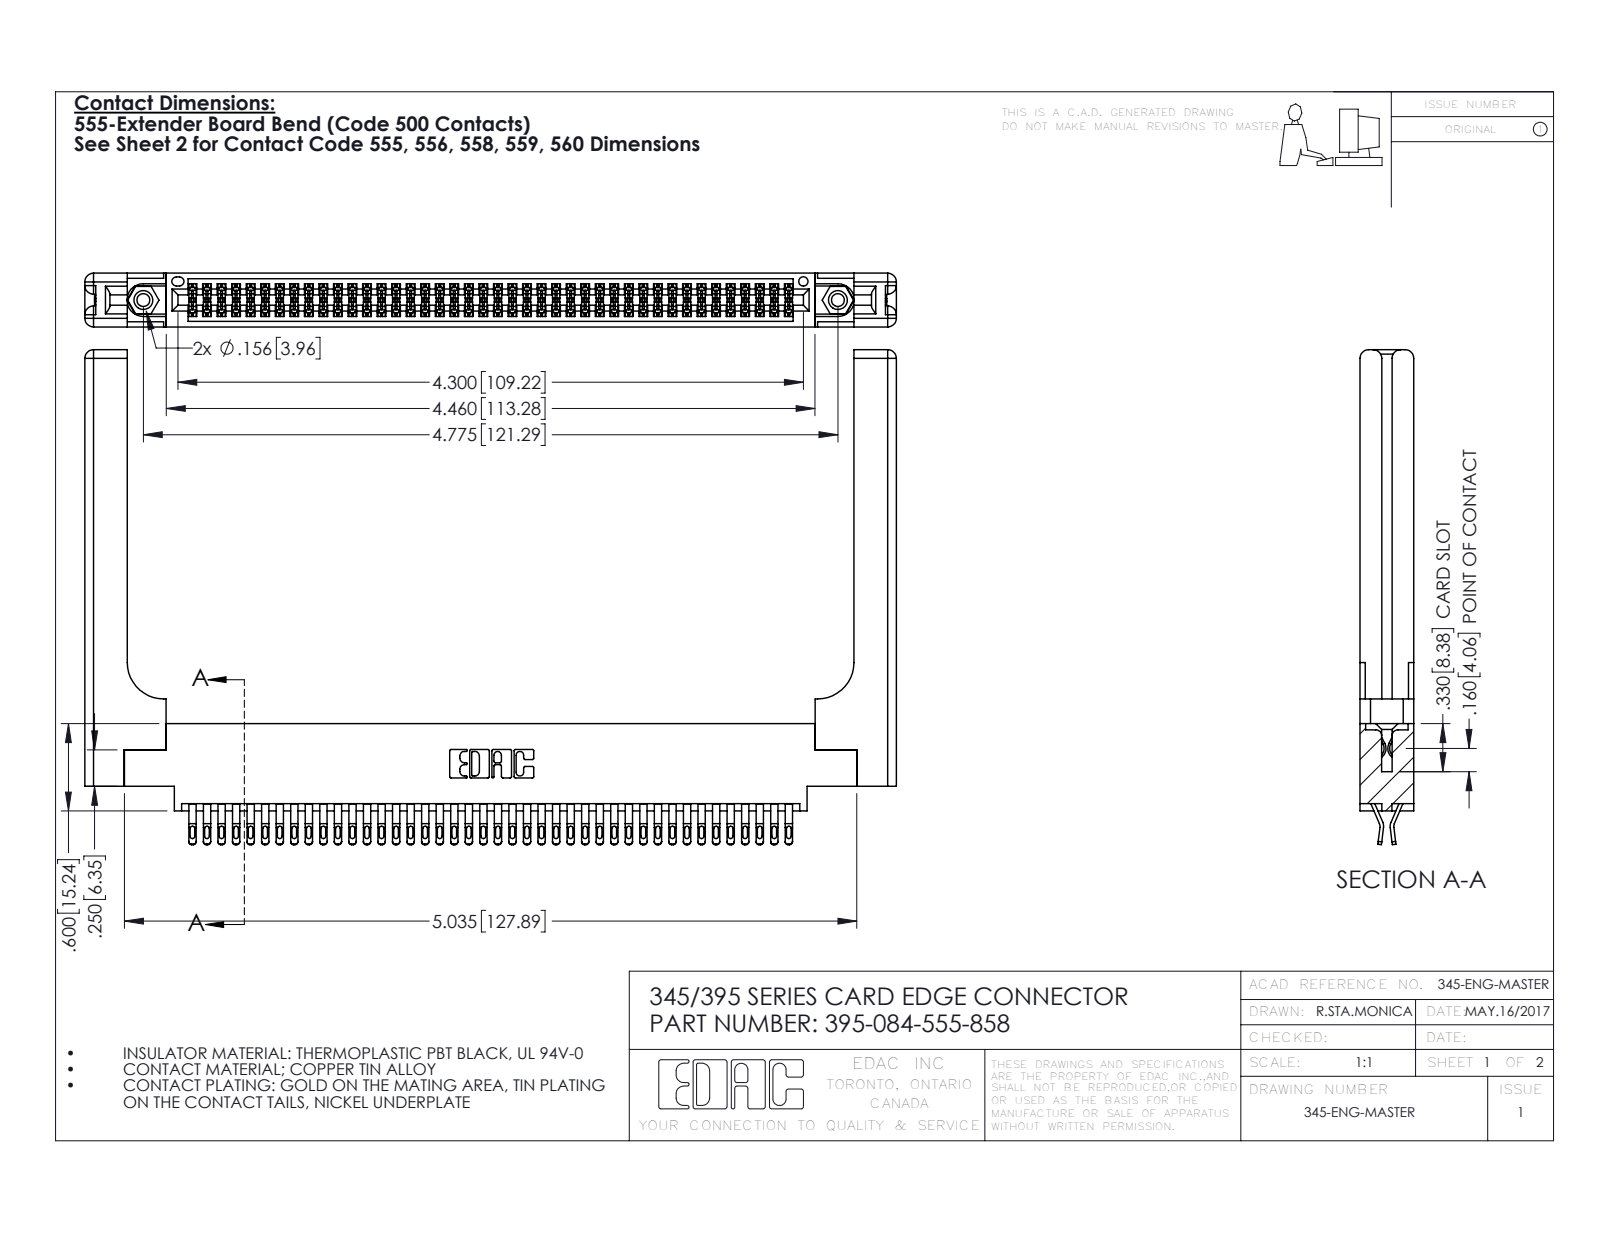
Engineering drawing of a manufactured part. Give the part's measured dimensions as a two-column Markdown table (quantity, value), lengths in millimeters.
| quantity | value |
| --- | --- |
| part name | 345-250-001_345-250-001-102; 345 Part_0.170 Offset - 0.156 Dia-TH; 345-292-001_555 Tail; 345-220-058_345-220-058 (+1 more) |
| STEP written by | SolidWorks 2016 (CONFIG_CONTROL_DESIGN) |
| units | millimeters |
| bodies | 89 solids, 5090 faces (2836 planar, 2194 cylindrical, 60 other) |
| overall size | 141.7 × 86.4 × 9.4 |
| volume | 22 370 mm³ |
| surface area | 26 590 mm² |
| round holes (diameter × count) | 2.3 × 2, 3.2 × 2, 4 × 2, 1.6 × 1 |
| round bosses / shafts (diameter × count) | 3.9 × 2 |
| partial cylindrical surfaces (radius × count) | 0.4 × 210, 0.5 × 168, 0.2 × 126, 0.3 × 22, 1.5 × 16, 0.2 × 6, 0.8 × 6, 0.7 × 3 |
| main face-to-face distances | 9.4, 1.8, 7.6, 0.6, 2.5, 6.9, 5.1, 5.7, 3.8, 3.8 |
| hole center spacings | 6.9, 115.3, 121.3 |
